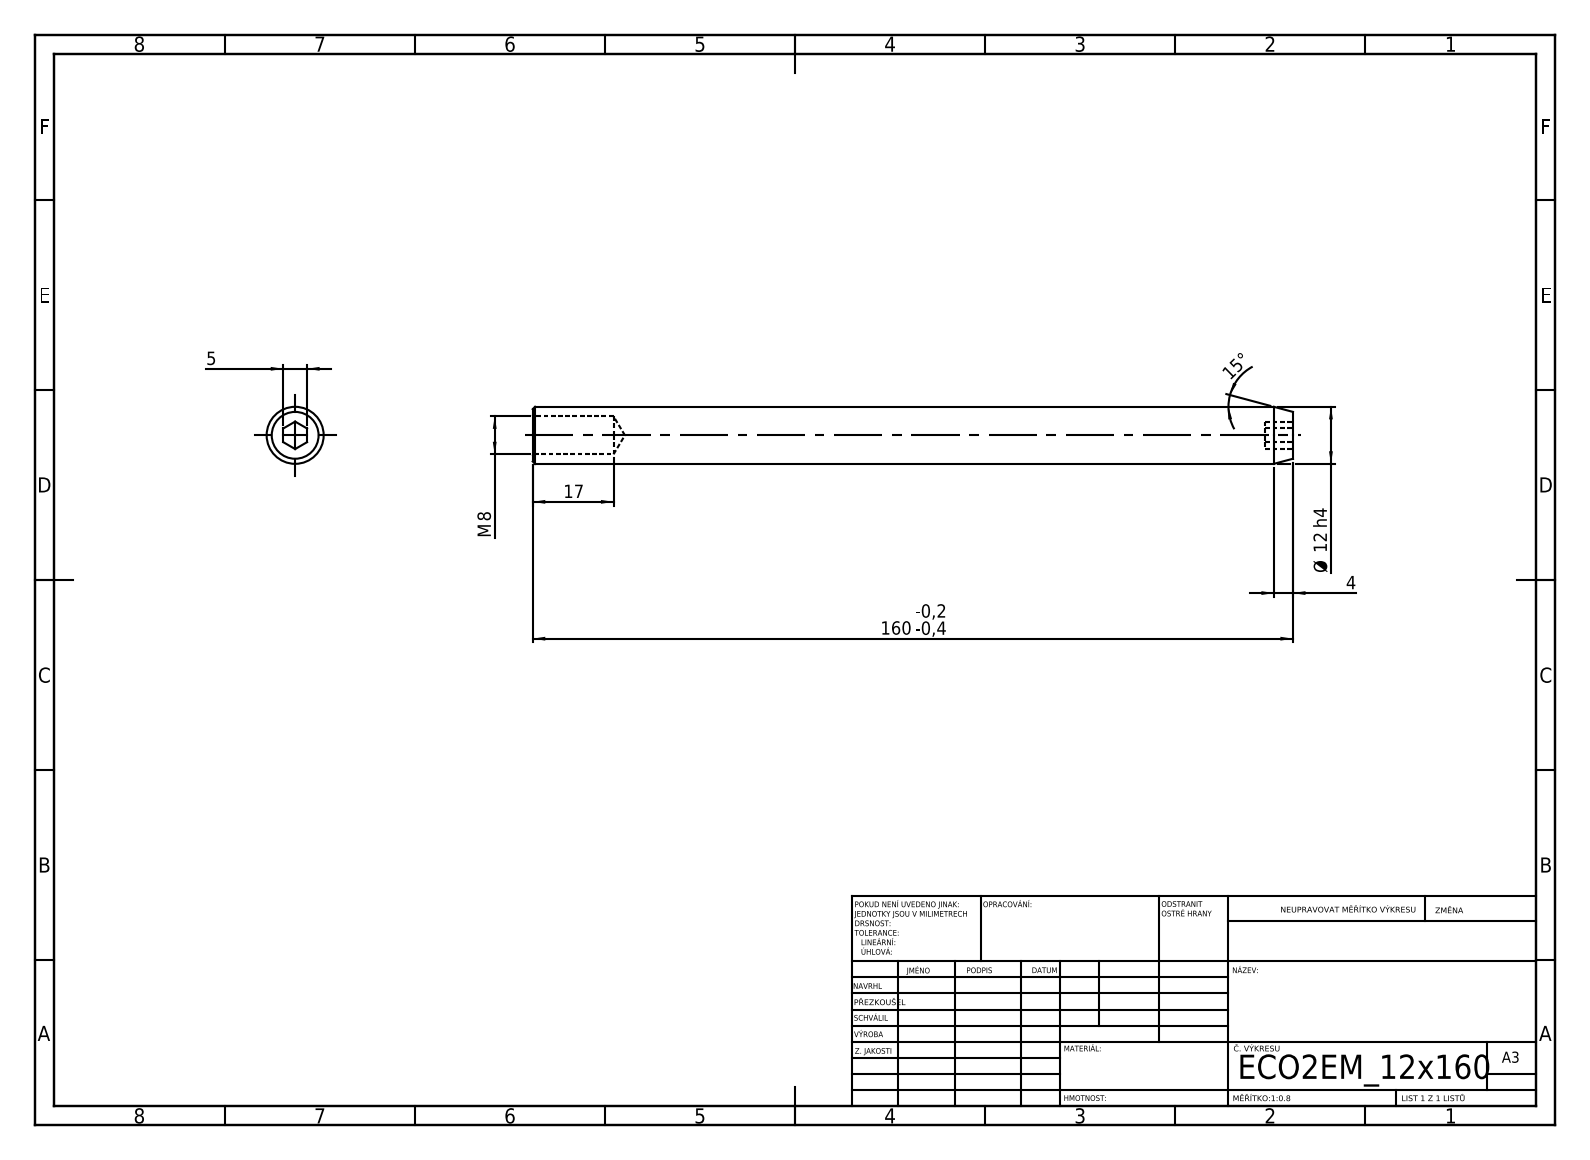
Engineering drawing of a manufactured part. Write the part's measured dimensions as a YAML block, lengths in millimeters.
step_written_by: "SolidWorks 2019 (CONFIG_CONTROL_DESIGN)"
units: millimeters
bodies: {solids: 1, faces: 21, planar: 9, cylindrical: 4, other: 8}
overall_size: [160, 12, 12]
volume: 16994
surface_area: 6734
round_holes:
  - {diameter: 8, count: 1}
round_bosses_or_shafts:
  - {diameter: 12, count: 1}
face_to_face_distances: [5, 160, 5.8, 154.2]
